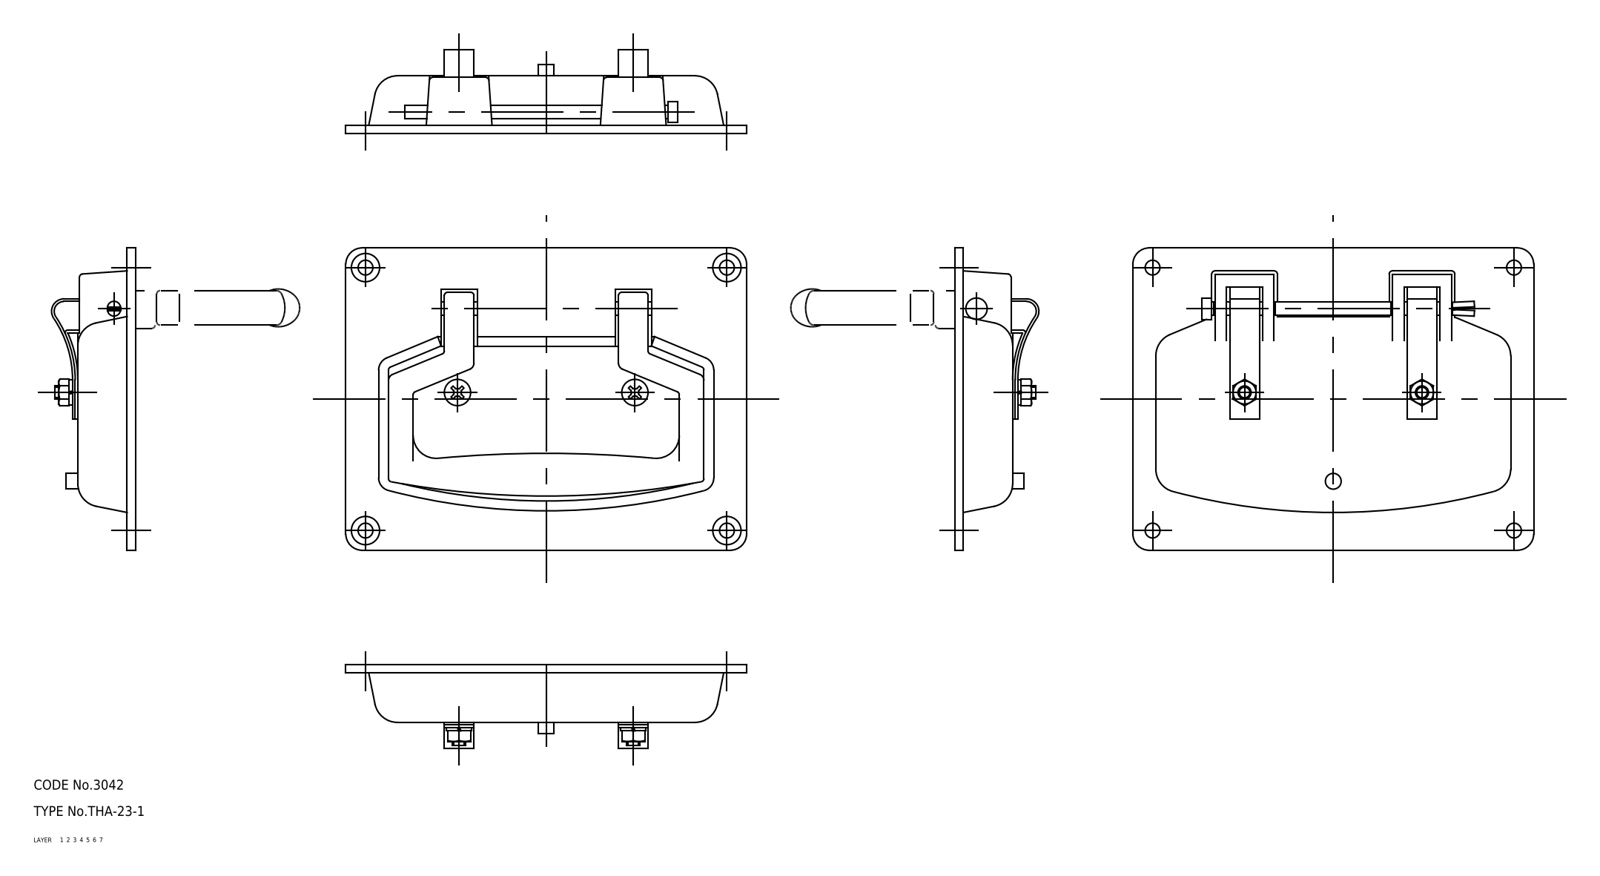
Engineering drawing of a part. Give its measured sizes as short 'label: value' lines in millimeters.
name: leaf spring_B; leaf spring_A; washer; nut (+6 more)
written by: CADfix (AUTOMOTIVE_DESIGN)
unit: mm
bodies: 14 solids, 491 faces (0 planar, 0 cylindrical, 491 other)
size: 122 × 92 × 25.5
volume: 66 223 mm³; area: 45 070 mm²
